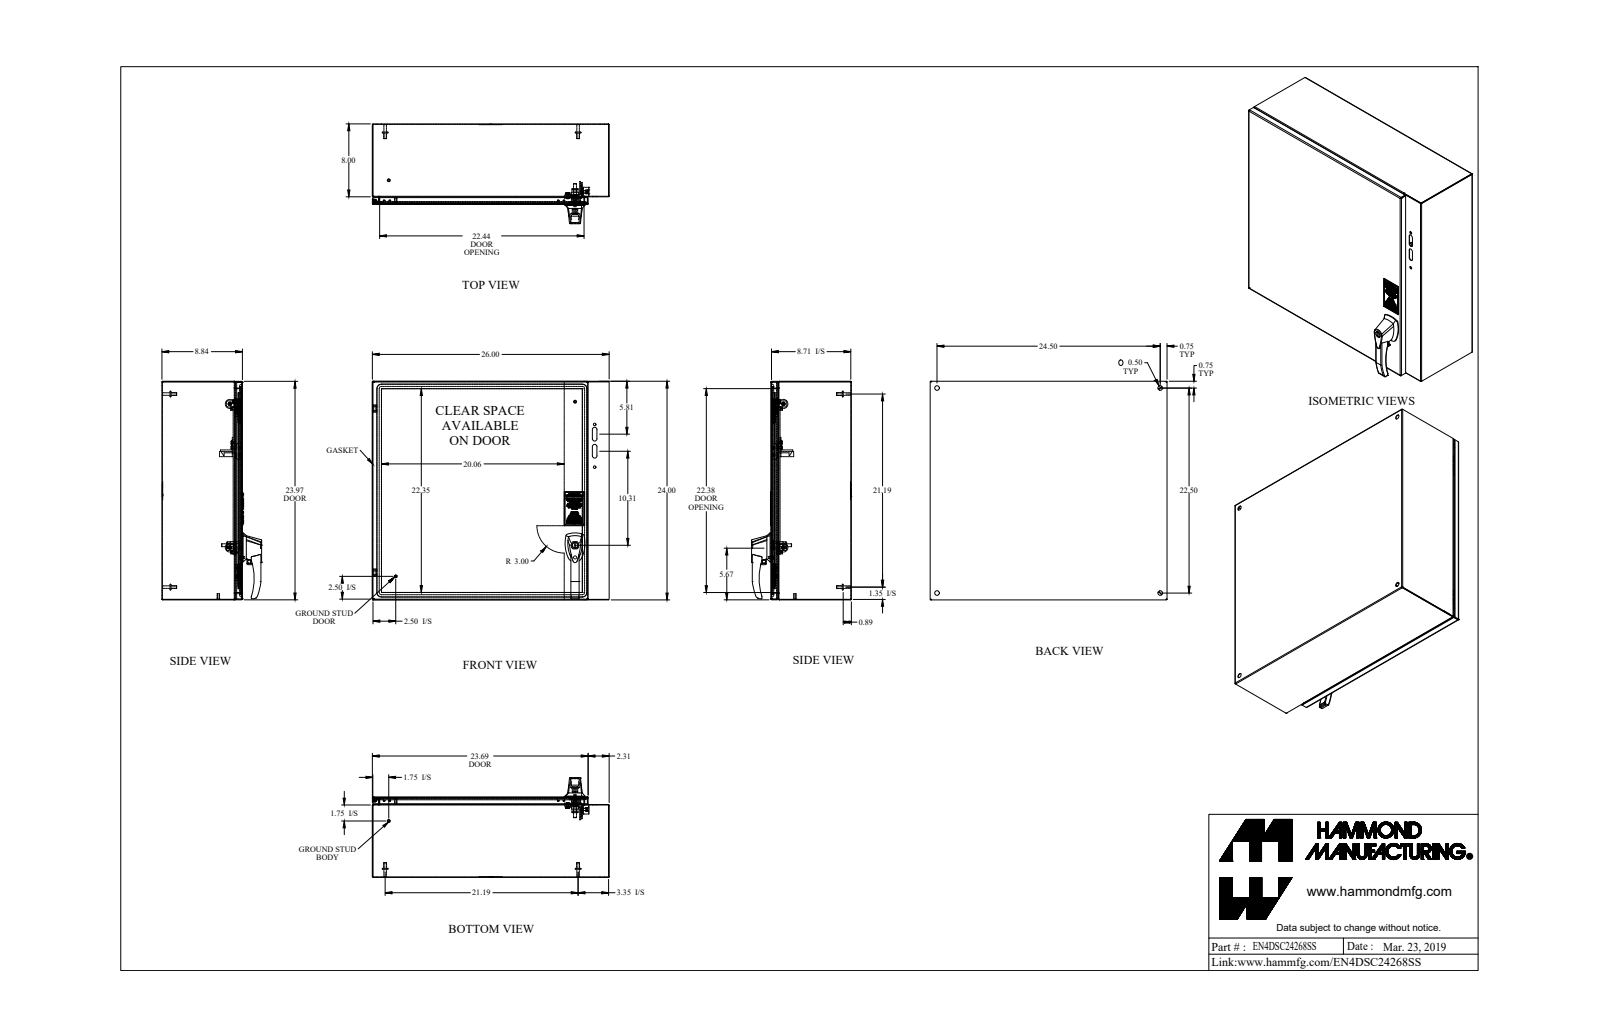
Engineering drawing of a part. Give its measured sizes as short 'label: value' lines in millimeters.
name: EN4DSC24268SS
written by: SolidWorks 2019 (AUTOMOTIVE_DESIGN)
unit: mm
bodies: 47 solids, 1047 faces (610 planar, 306 cylindrical, 131 other)
size: 660.4 × 609.6 × 278.2
volume: 2 689 000 mm³; area: 3 211 000 mm²
holes: 4× ⌀4.5, 4× ⌀12.7, 2× ⌀4, 2× ⌀4.4, 2× ⌀5.5, 2× ⌀6.4, 2× ⌀6.7, 2× ⌀7.1, 2× ⌀10.5, 1× ⌀4.4, 1× ⌀5, 1× ⌀5.9
bosses: 7× ⌀6.4, 4× ⌀9.5, 4× ⌀8, 4× ⌀6.9, 4× ⌀4, 2× ⌀25.4, 2× ⌀15.9, 2× ⌀15.9
rounds: 17× R0.7, 17× R2.2, 14× R0.8, 14× R6.4, 12× R1.1, 12× R2.1, 11× R3.2, 6× R1.5
face distances: 1.4, 1.8, 221.2, 222.6, 223, 224.5, 608.2, 659, 201.8, 606.7
hole spacings: 400.1, 28.2, 571.5, 622.3, 844.9, 13.2, 19.1, 20.8
